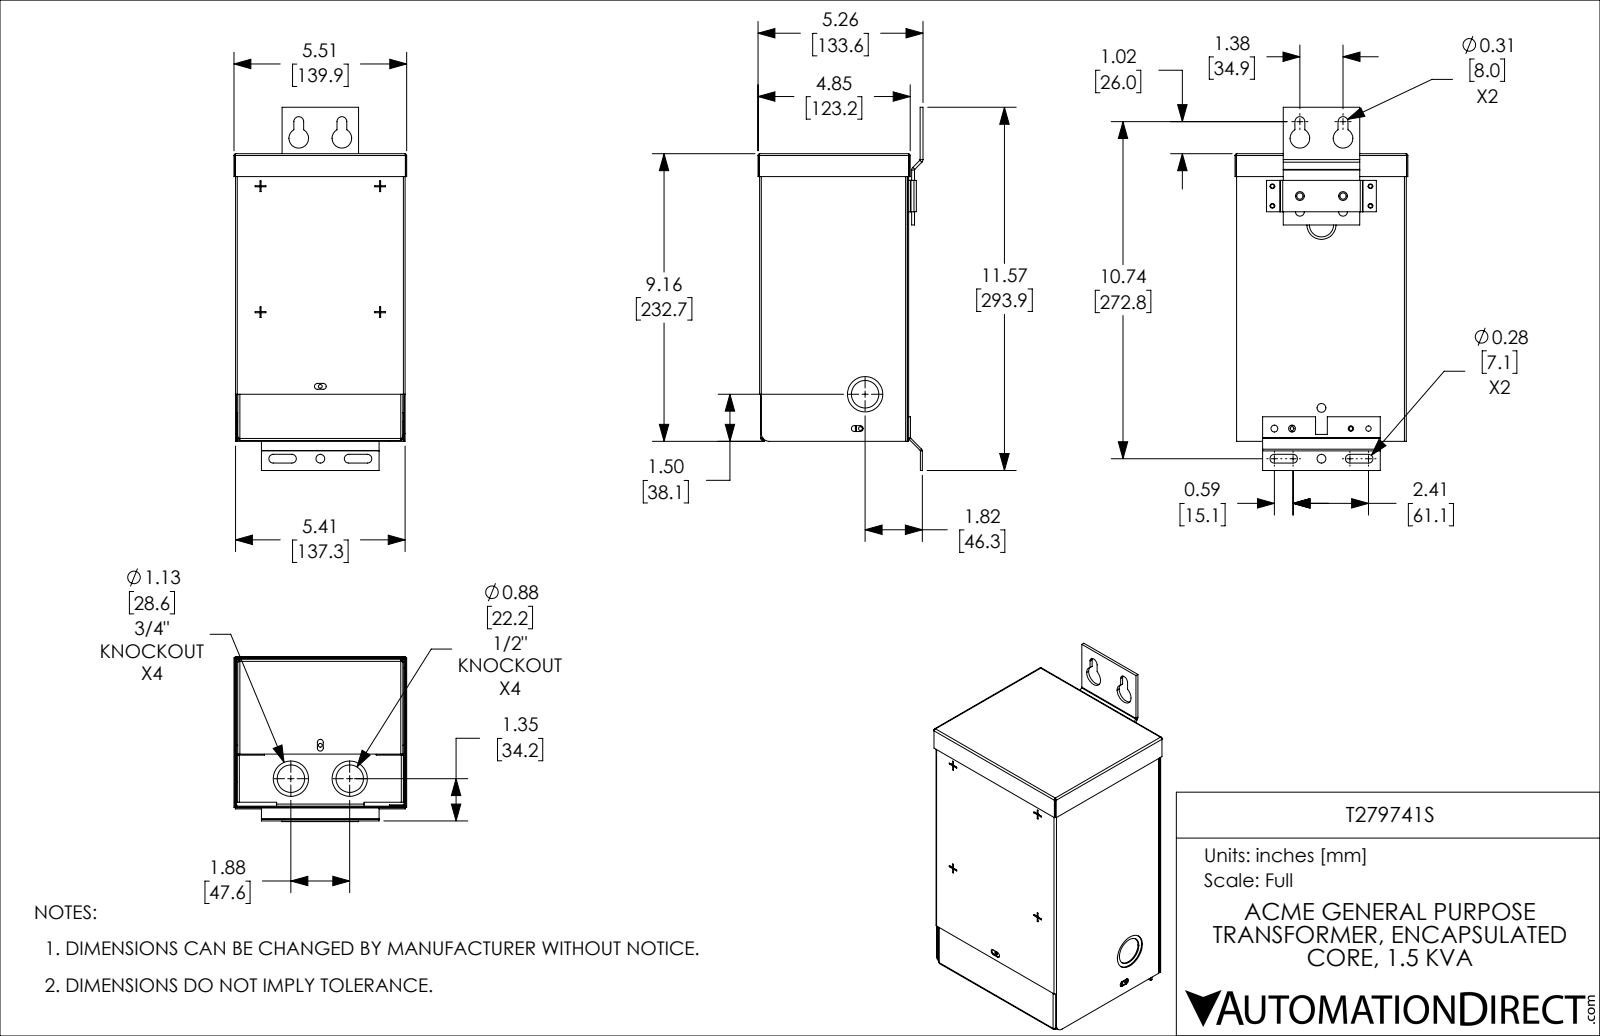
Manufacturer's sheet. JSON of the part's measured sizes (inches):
{"part_name": "T279741S", "step_written_by": "SolidWorks 2021 (CONFIG_CONTROL_DESIGN)", "units": "inches", "bodies": {"solids": 7, "faces": 521, "planar": 329, "cylindrical": 152, "other": 40}, "overall_size": [11.57, 5.508, 5.259], "volume_in3": 10.83, "surface_area_in2": 570.5, "round_holes": [[0.281, 6], [0.12, 5], [0.875, 3], [1.125, 3], [0.172, 2], [0.187, 2], [0.201, 2], [0.219, 2], [0.625, 2]], "round_bosses_or_shafts": [[1.173, 1], [0.923, 1]], "partial_cylinders_radius": [[0.02, 10], [0.094, 10], [0.031, 8], [0.056, 8], [0.067, 8], [0.015, 4], [0.075, 4], [0.141, 4]], "face_to_face_distances": [0.036, 4.714, 5.37, 4.678, 5.335, 5.406, 4.75, 9.1, 0.051, 0.087], "hole_center_spacings": [1.375, 0.5, 0.563, 1.145, 1.342, 1.417, 1.463, 1.638]}
